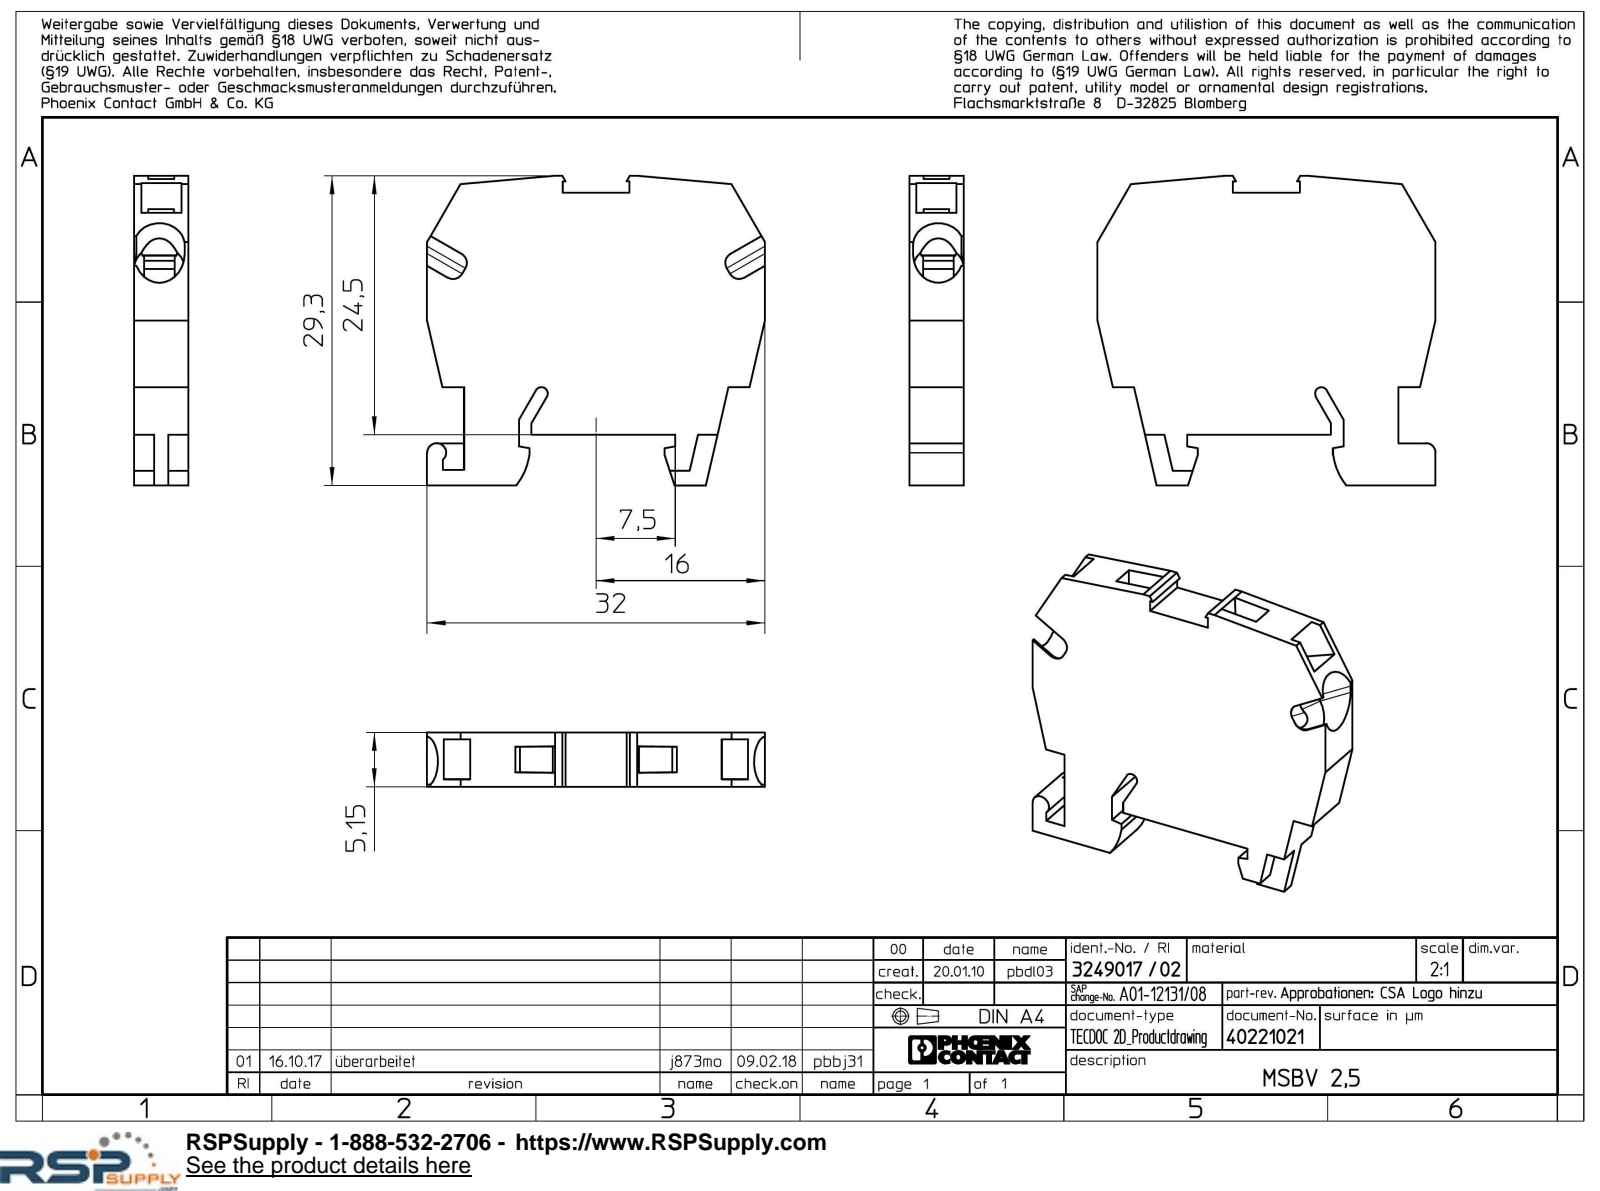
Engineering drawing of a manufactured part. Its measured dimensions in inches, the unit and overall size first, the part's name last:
Units: inches
Overall size (bounding box): 1.26 × 1.154 × 0.203
Partial cylindrical surfaces — rounded edges, fillets, slot ends (radius × count): R0.039 ×8, R0.094 ×4, R0.035 ×1, R0.236 ×1
Main face-to-face distances: 0.203, 0.026, 0.177, 0.175, 0.15, 0.028, 0.189, 0.249, 0.037, 0.077
Volume: 0.195 in³ · Surface area: 4.521 in²
Bodies: 1 solid, 129 faces (107 planar, 14 cylindrical, 8 other)
Part name (STEP PRODUCT): MSBV_2.5-select
STEP written by: Creo Elements/Direct Modeling 18.1I 14-Aug-2016 (C) Parametric Technology GmbH (AUTOMOTIVE_DESIGN)
